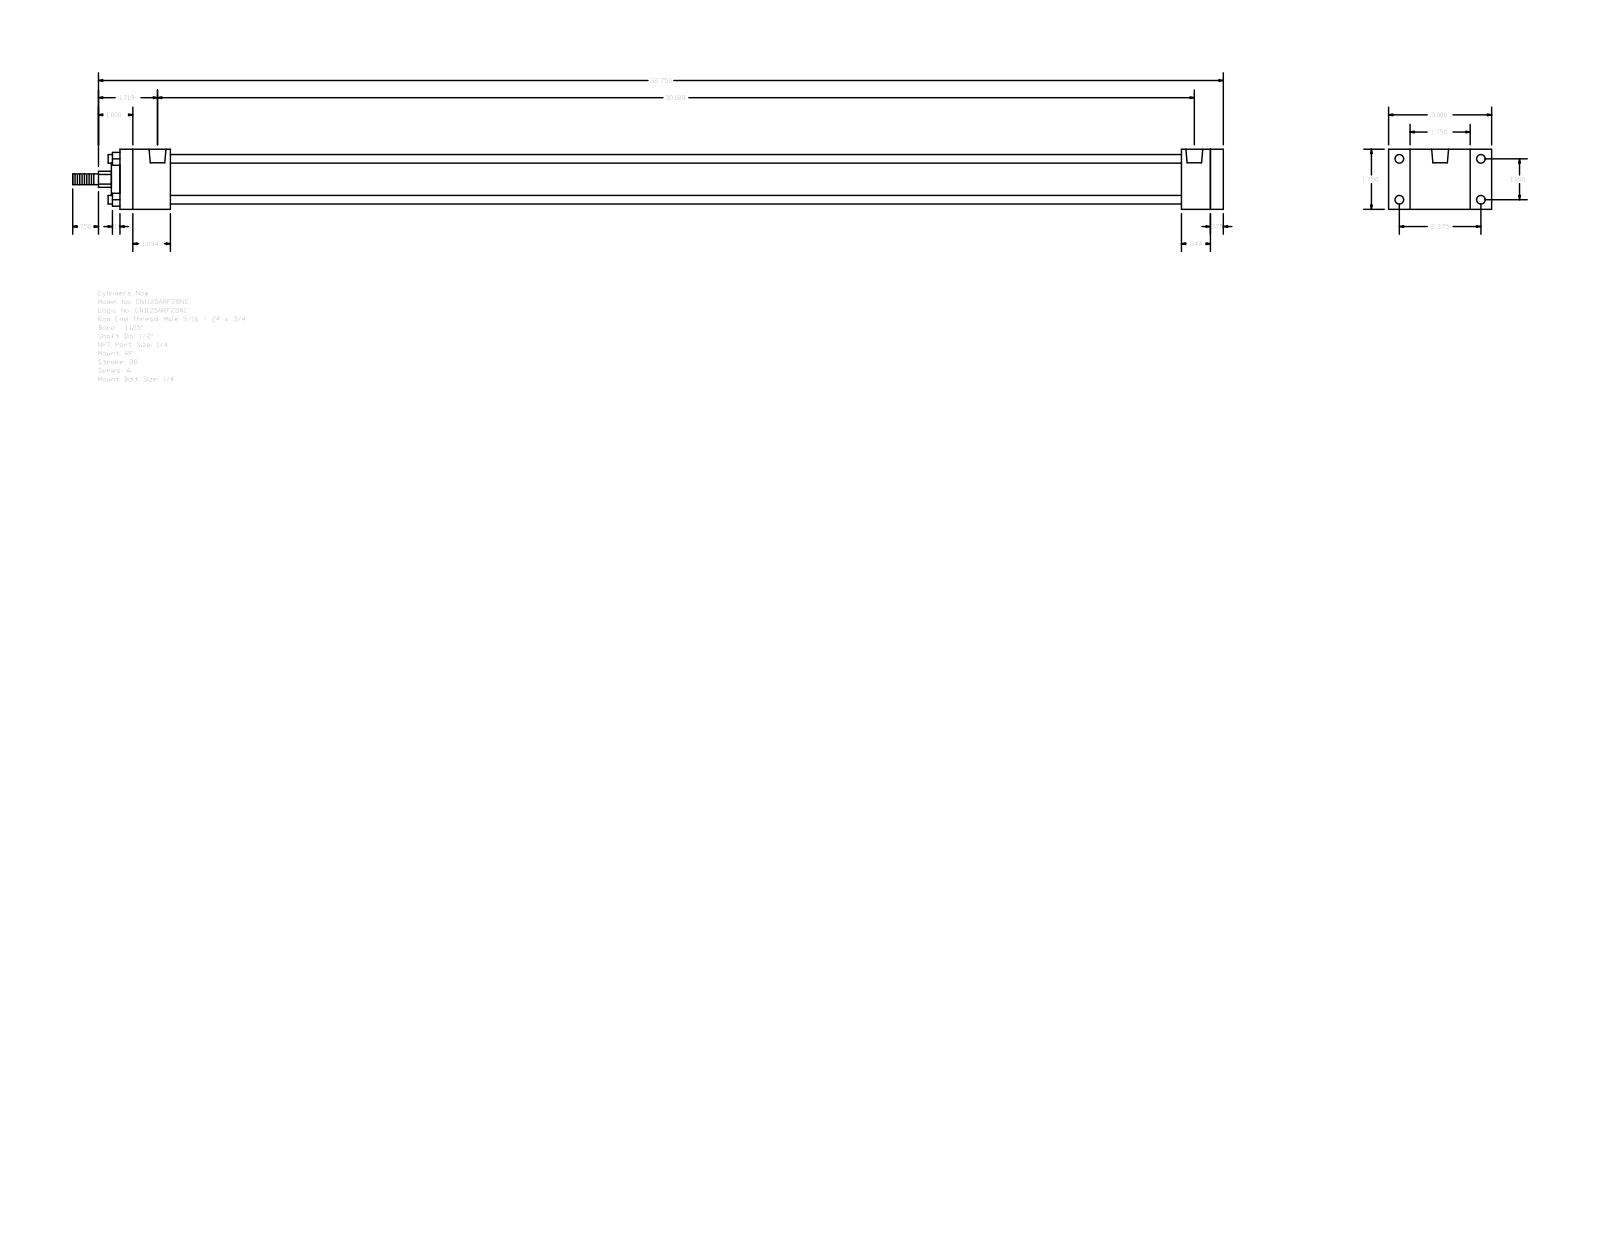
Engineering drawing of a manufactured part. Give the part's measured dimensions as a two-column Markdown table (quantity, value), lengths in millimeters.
| quantity | value |
| --- | --- |
| part name | A_RF__0112_0.5 |
| STEP written by | GSSL Pune (CONFIG_CONTROL_DESIGN) |
| units | millimeters |
| bodies | 0 solids, 92 faces (64 planar, 28 cylindrical, 0 other) |
| overall size | 850.9 × 76.2 × 44.45 |
| round holes (diameter × count) | 5.56 × 4, 6.35 × 4, 12.49 × 2 |
| round bosses / shafts (diameter × count) | 6.35 × 4, 31.88 × 1, 23.81 × 1, 12.7 × 1, 7.94 × 1 |
| partial cylindrical surfaces (radius × count) | 5.94 × 1 |
| main face-to-face distances | 44.46, 9.52, 806.45, 815.97, 37.3, 785.01, 747.71, 769.15, 778.67, 21.44 |
| hole center spacings | 30.22, 60.32, 67.47, 763.59, 1.58, 1.59, 765.17, 765.18 |
